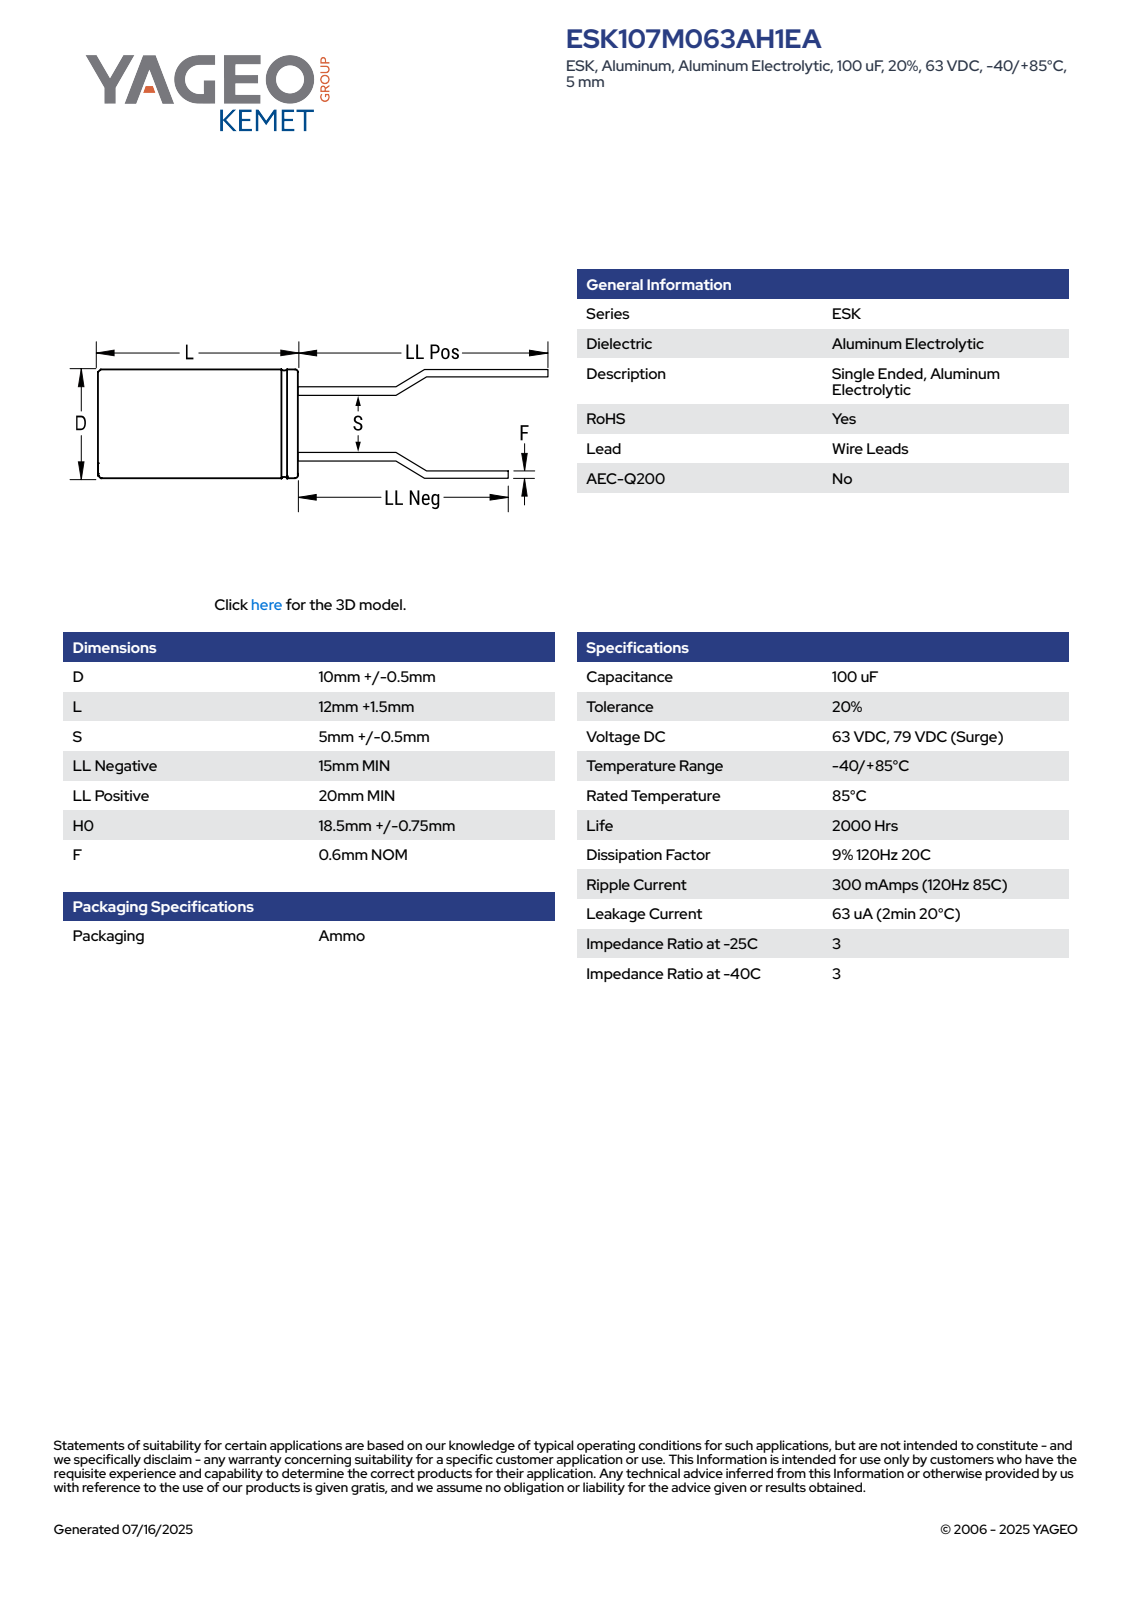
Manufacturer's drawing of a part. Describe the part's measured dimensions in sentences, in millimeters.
The part is named "CAR_KTRS_10X12_D10.5L13.5S5F0.6". Its 3-D file was written by "SolidWorks 2014 (AUTOMOTIVE_DESIGN)". It is 4 solids with 73 faces: 61 planar, 8 cylindrical and 4 other. Overall it measures 33.51 by 10.5 by 10.5 millimeters. Its volume is 1 167 cubic millimeters and its surface area 709 square millimeters. Round bosses or shafts: 2 of diameter 0.6, 1 of diameter 10.5. The main face-to-face distances are 13.5, 13.51, 28.51, 33.51, 28.5, 33.5, 15, 20, 5, 1.24.
